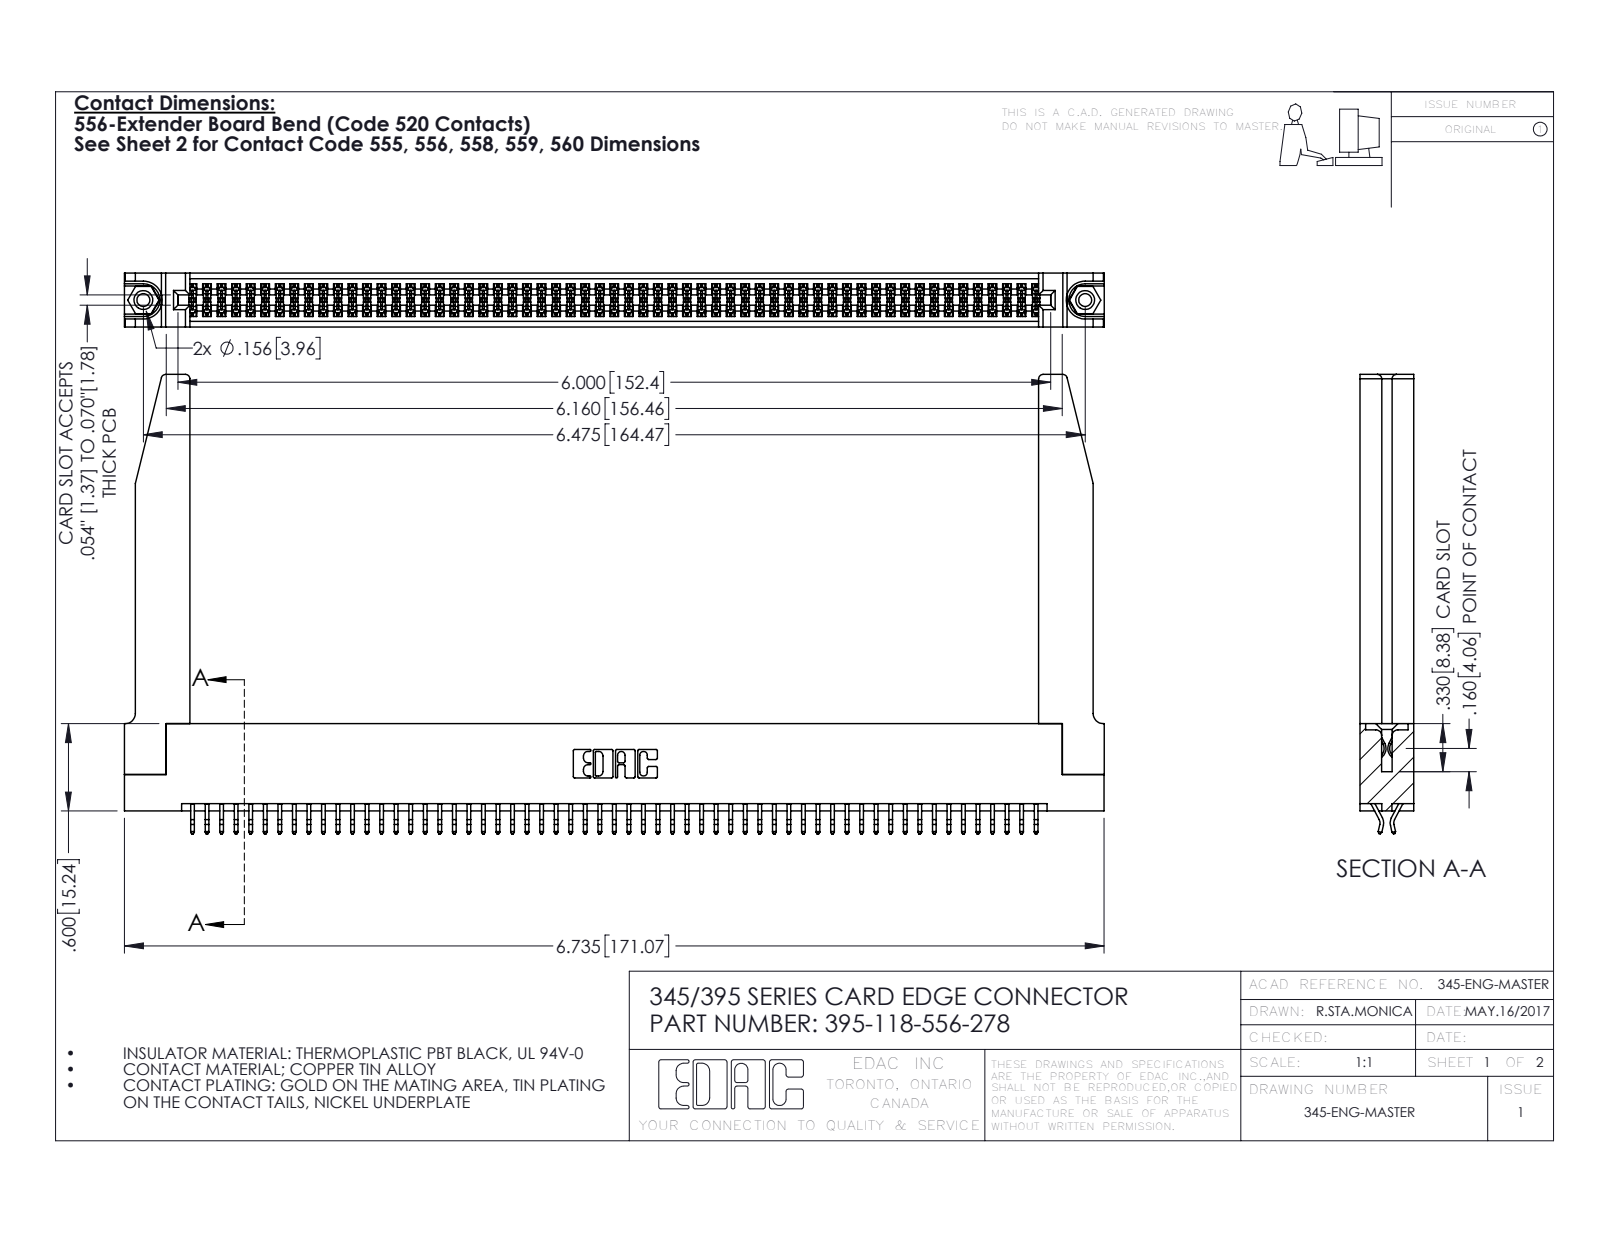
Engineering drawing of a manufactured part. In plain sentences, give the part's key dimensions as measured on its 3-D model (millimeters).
The part is named "345 Part_Flush Mounting Lugs - 0.156 Dia-TH; 345-250-001_345-250-001-102; 345-292-001_556 Tail; 345-220-078_345-220-078 (+1 more)". Its 3-D file was written by "SolidWorks 2016 (CONFIG_CONTROL_DESIGN)". It is 123 solids with 6968 faces: 4588 planar, 2328 cylindrical and 52 other. Overall it measures 171.1 by 80.2 by 9.4 millimeters. Its volume is 24 550 cubic millimeters and its surface area 31 860 square millimeters. Round holes: 2 of diameter 2.3, 2 of diameter 3.2, 2 of diameter 4, 1 of diameter 1.6. Round bosses or shafts: 2 of diameter 3.9. Partial cylindrical surfaces (rounded edges, fillets, slot ends): 177 of radius 0.2, 22 of radius 0.3, 8 of radius 0.8, 6 of radius 0.2, 6 of radius 0.8, 3 of radius 0.7, 2 of radius 0.3, 2 of radius 0.4. The main face-to-face distances are 1.8, 9.4, 7.6, 5.1, 0.6, 2.5, 6.9, 5.7, 4.4, 3.8. The hole center spacings are 6.9, 158.5, 164.5.
